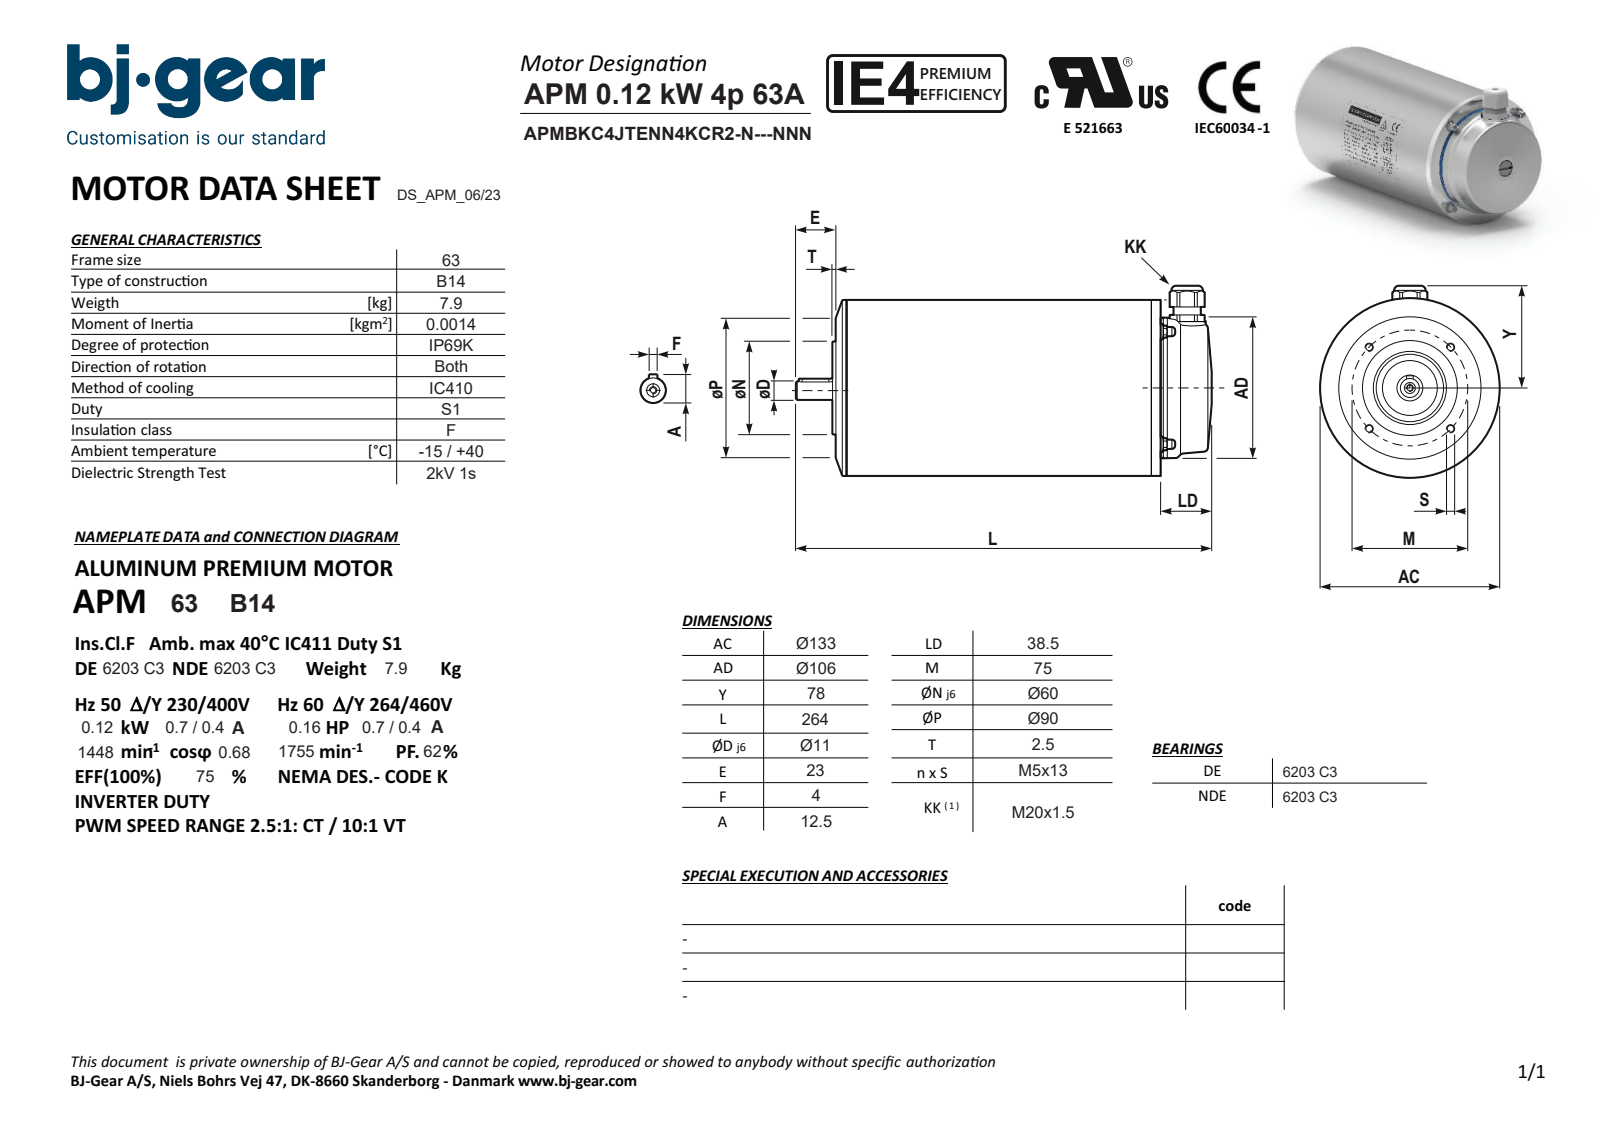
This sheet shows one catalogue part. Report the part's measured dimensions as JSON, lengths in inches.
{"part_name": "APMBKC4JTENN4KCR2-N---NNN", "step_written_by": "Solid Edge (AUTOMOTIVE_DESIGN)", "units": "inches", "bodies": {"solids": 1, "faces": 156, "planar": 75, "cylindrical": 50, "other": 31}, "overall_size": [10.394, 5.642, 5.22], "volume_in3": 187.6, "surface_area_in2": 197.3, "round_holes": [[0.163, 4], [0.128, 1], [0.169, 1], [0.63, 1], [1.102, 1], [2.047, 1]], "round_bosses_or_shafts": [[0.453, 4], [0.276, 4], [5.22, 1], [5.22, 1], [4.173, 1], [2.362, 1], [0.933, 1], [0.811, 1]], "partial_cylinders_radius": [[0.079, 2], [0.52, 1]], "face_to_face_distances": [7.972, 7.756, 0.217, 0.315, 0.098, 8.071, 1.516, 9.272, 9.488, 9.587], "hole_center_spacings": [1.476, 2.088, 2.953]}
